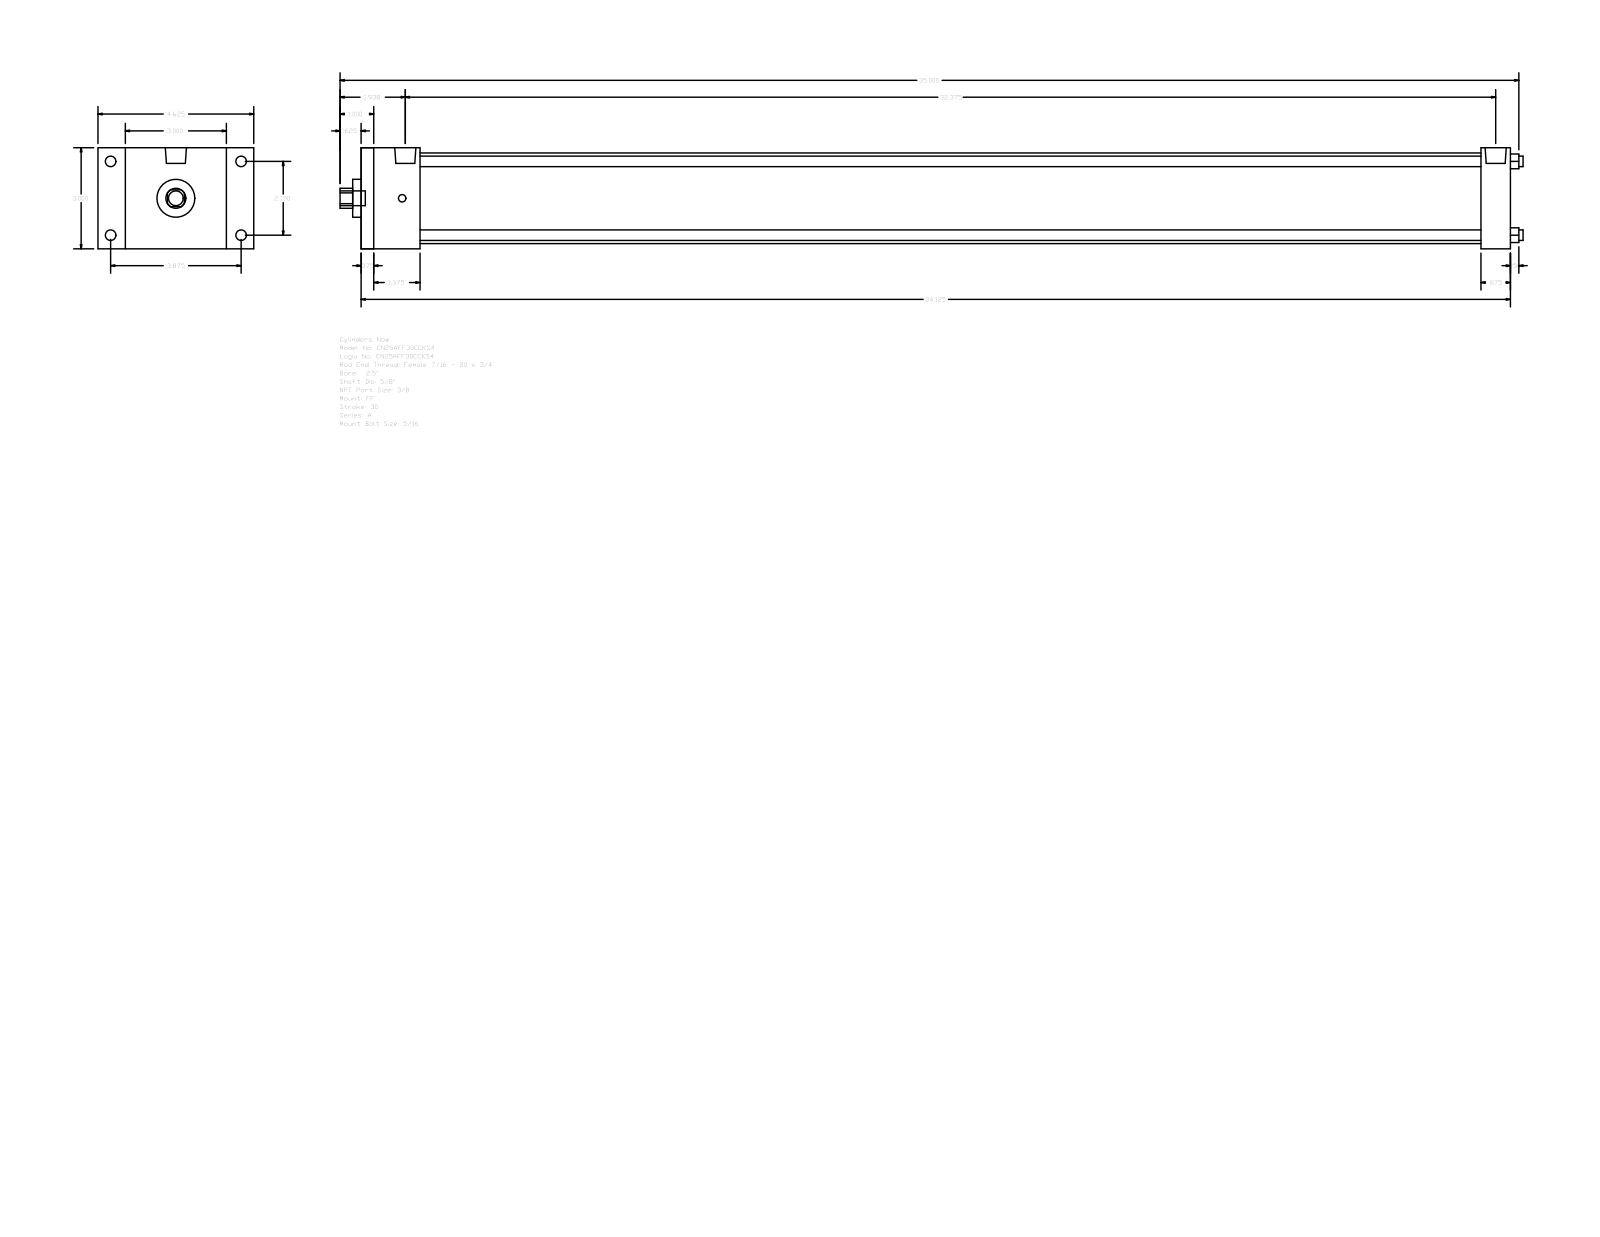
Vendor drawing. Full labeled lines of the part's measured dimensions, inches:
Part name (STEP PRODUCT): A_FF__0250_0.625
STEP written by: GSSL Pune (CONFIG_CONTROL_DESIGN)
Units: inches
Bodies: 0 solids, 92 faces (64 planar, 28 cylindrical, 0 other)
Overall size (bounding box): 35.125 × 4.625 × 3
Round holes (diameter × count): ⌀0.313 ×4, ⌀0.625 ×1, ⌀1.125 ×1, ⌀2.69 ×1
Round bosses / shafts (diameter × count): ⌀0.313 ×4, ⌀0.219 ×4, ⌀0.627 ×2, ⌀0.437 ×1
Partial cylindrical surfaces — rounded edges, fillets, slot ends (radius × count): R0.297 ×1
Main face-to-face distances: 3, 34.125, 0.375, 33.75, 1.75, 33.25, 1.375, 32.875, 31.5, 32.375
Hole centre spacings: 1.548, 2.19, 3.097
